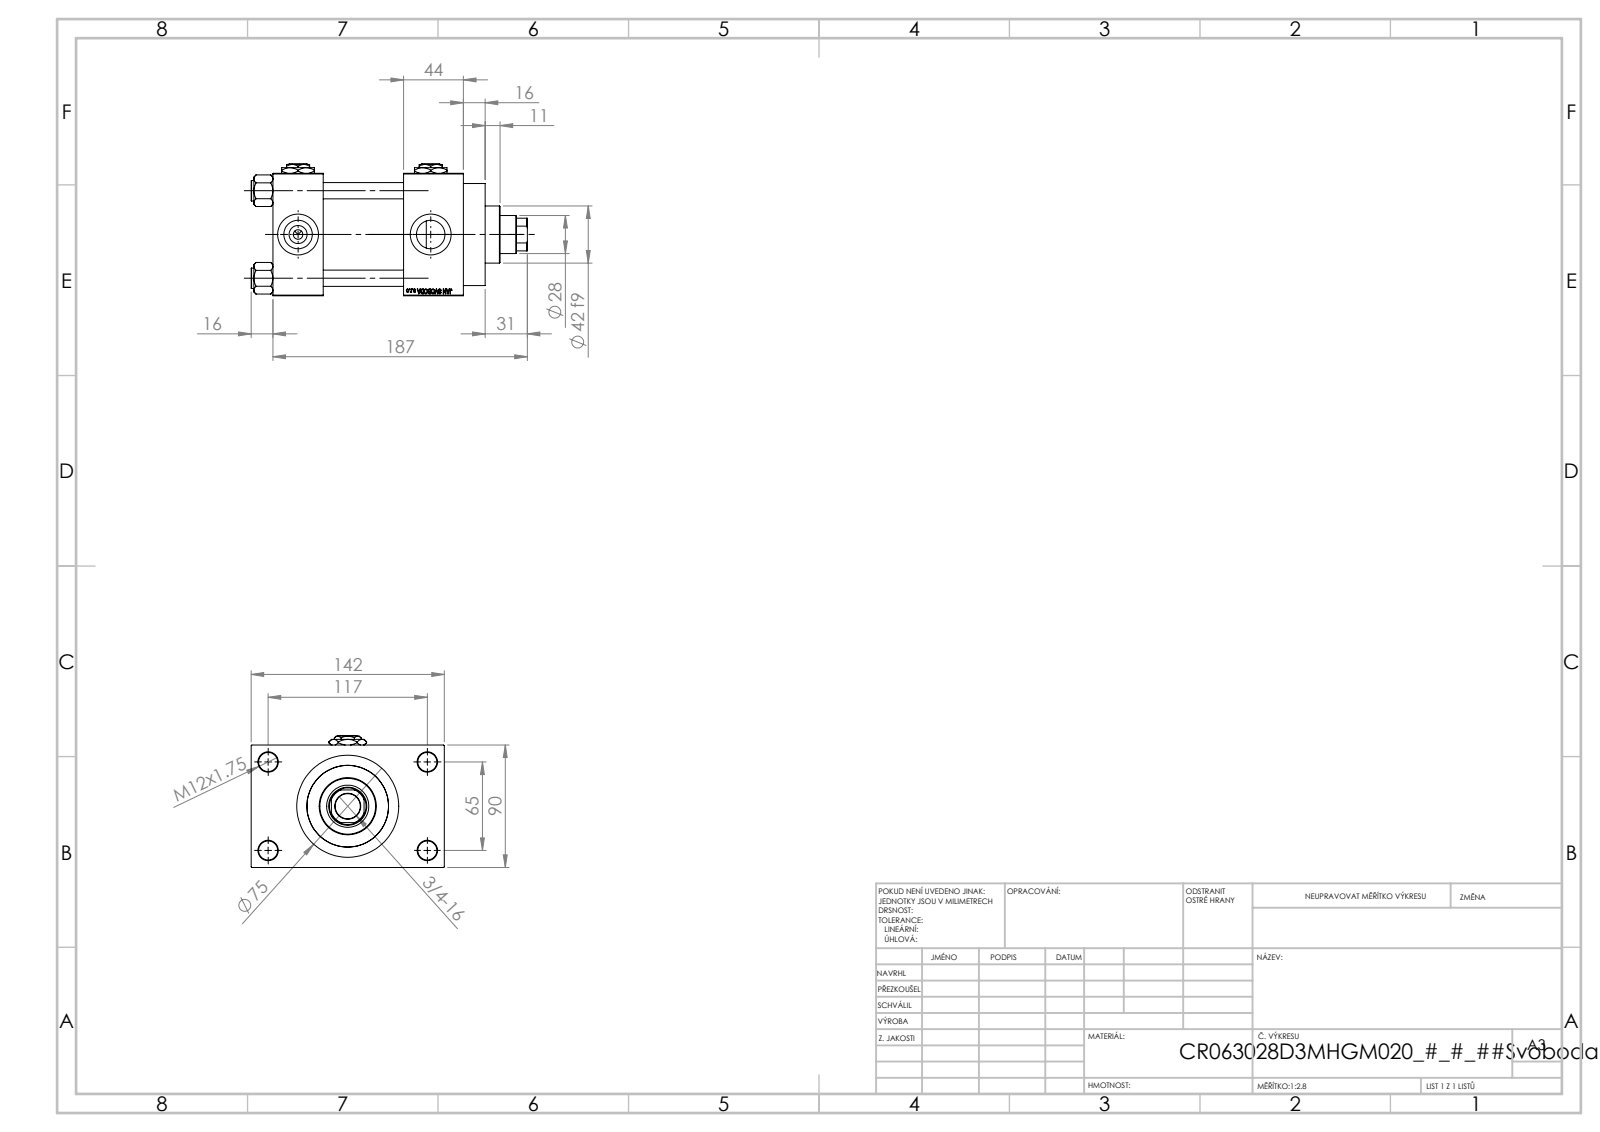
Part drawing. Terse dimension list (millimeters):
name: V215CR_VCP_D; NUT_M5_D; V215CR_D_Body; Zatka_pro_OIL_PORT (+2 more)
written by: SolidWorks 2019 (CONFIG_CONTROL_DESIGN)
unit: mm
bodies: 13 solids, 1204 faces (545 planar, 99 cylindrical, 560 other)
size: 203 × 142 × 97
volume: 1 091 000 mm³; area: 204 942 mm²
holes: 4× ⌀12, 4× ⌀14, 4× ⌀20.96, 4× ⌀30, 3× ⌀7, 1× ⌀18.5, 1× ⌀28, 1× ⌀31, 1× ⌀50, 1× ⌀60, 1× ⌀63
bosses: 4× ⌀15, 1× ⌀75, 1× ⌀69, 1× ⌀42
rounds: 1× R13.5
face distances: 90, 59, 37, 96, 140, 103, 44, 26, 116, 16
hole spacings: 26.35, 45.47, 64.3, 66.92, 69.81, 90.65, 111.34, 65
